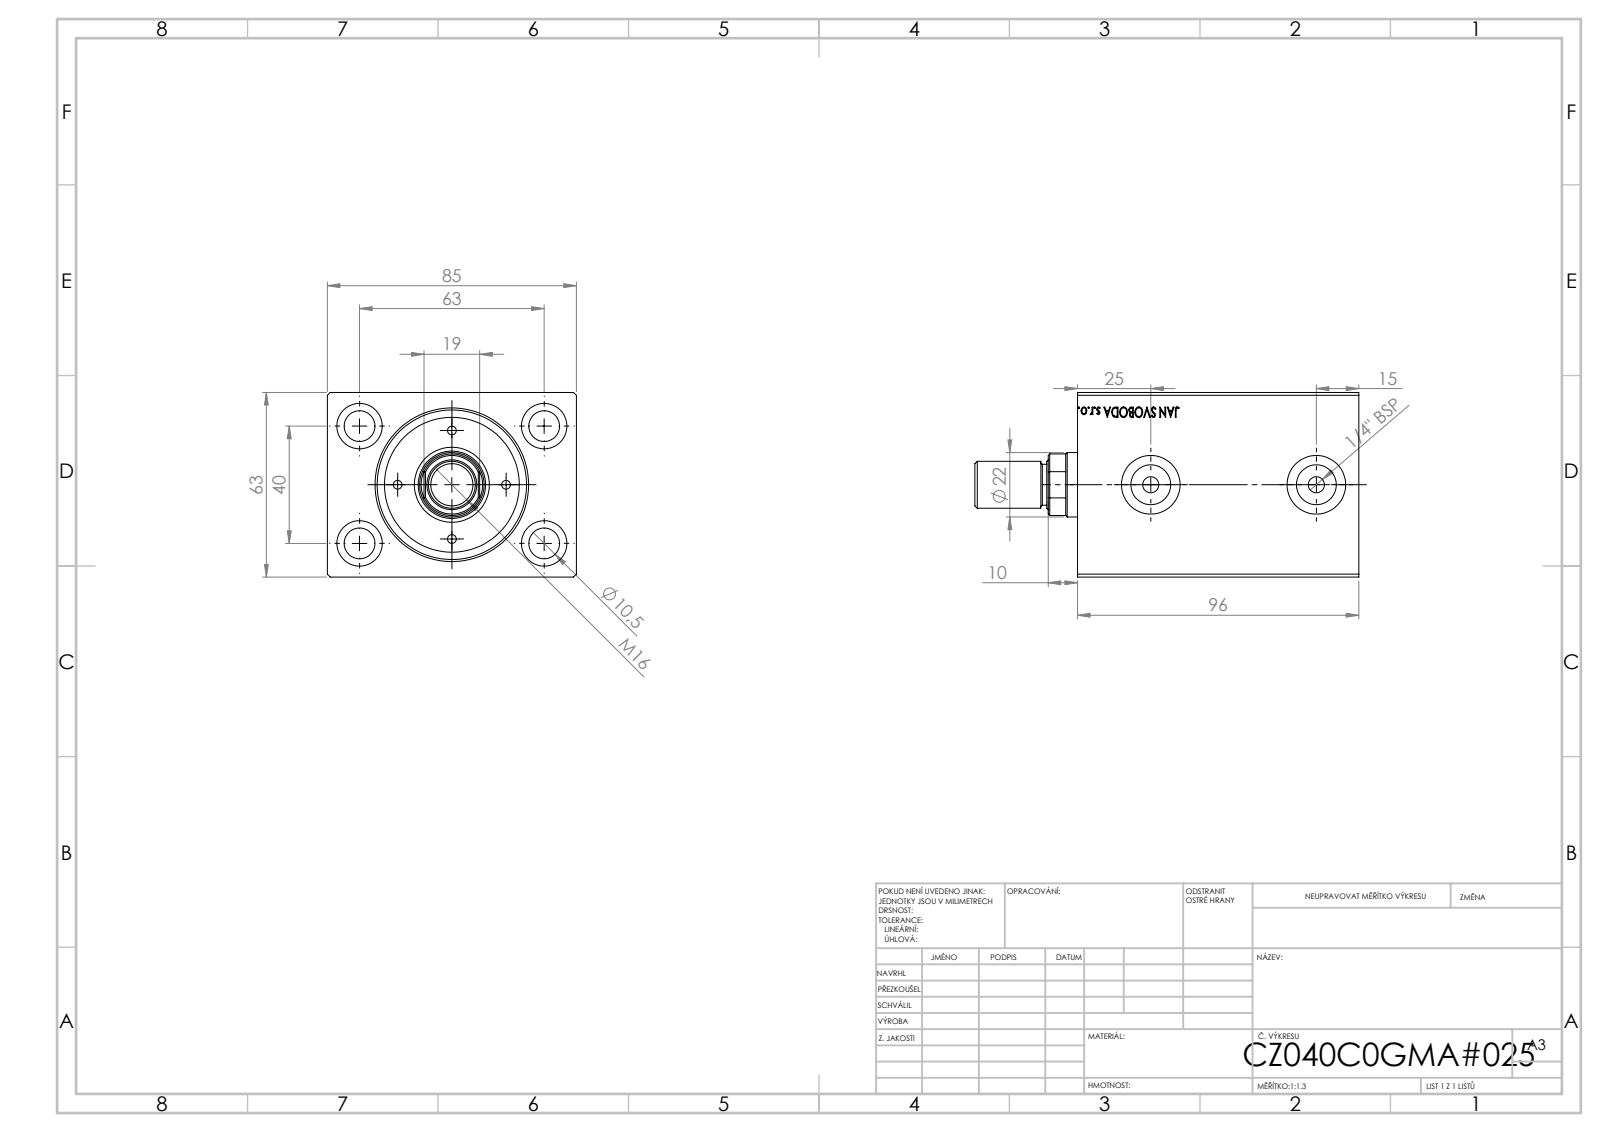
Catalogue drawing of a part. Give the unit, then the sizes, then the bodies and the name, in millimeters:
Units: millimetres
Overall size (bounding box): 96 × 85 × 63
Round holes (diameter × count): ⌀10.5 ×4, ⌀15.5 ×4, ⌀5.5 ×2, ⌀8 ×2, ⌀13.6 ×2, ⌀20 ×2, ⌀36 ×1, ⌀40 ×1, ⌀51 ×1
Main face-to-face distances: 63, 85, 96, 80.7, 15.3, 95.8, 15.1, 10.33, 85.67, 10
Hole centre spacings: 37.31, 40, 63, 74.63, 36.5, 56.5
Volume: 358 328 mm³ · Surface area: 64 223 mm²
Bodies: 1 solid, 825 faces (397 planar, 46 cylindrical, 382 other)
STEP written by: SolidWorks 2019 (CONFIG_CONTROL_DESIGN)
